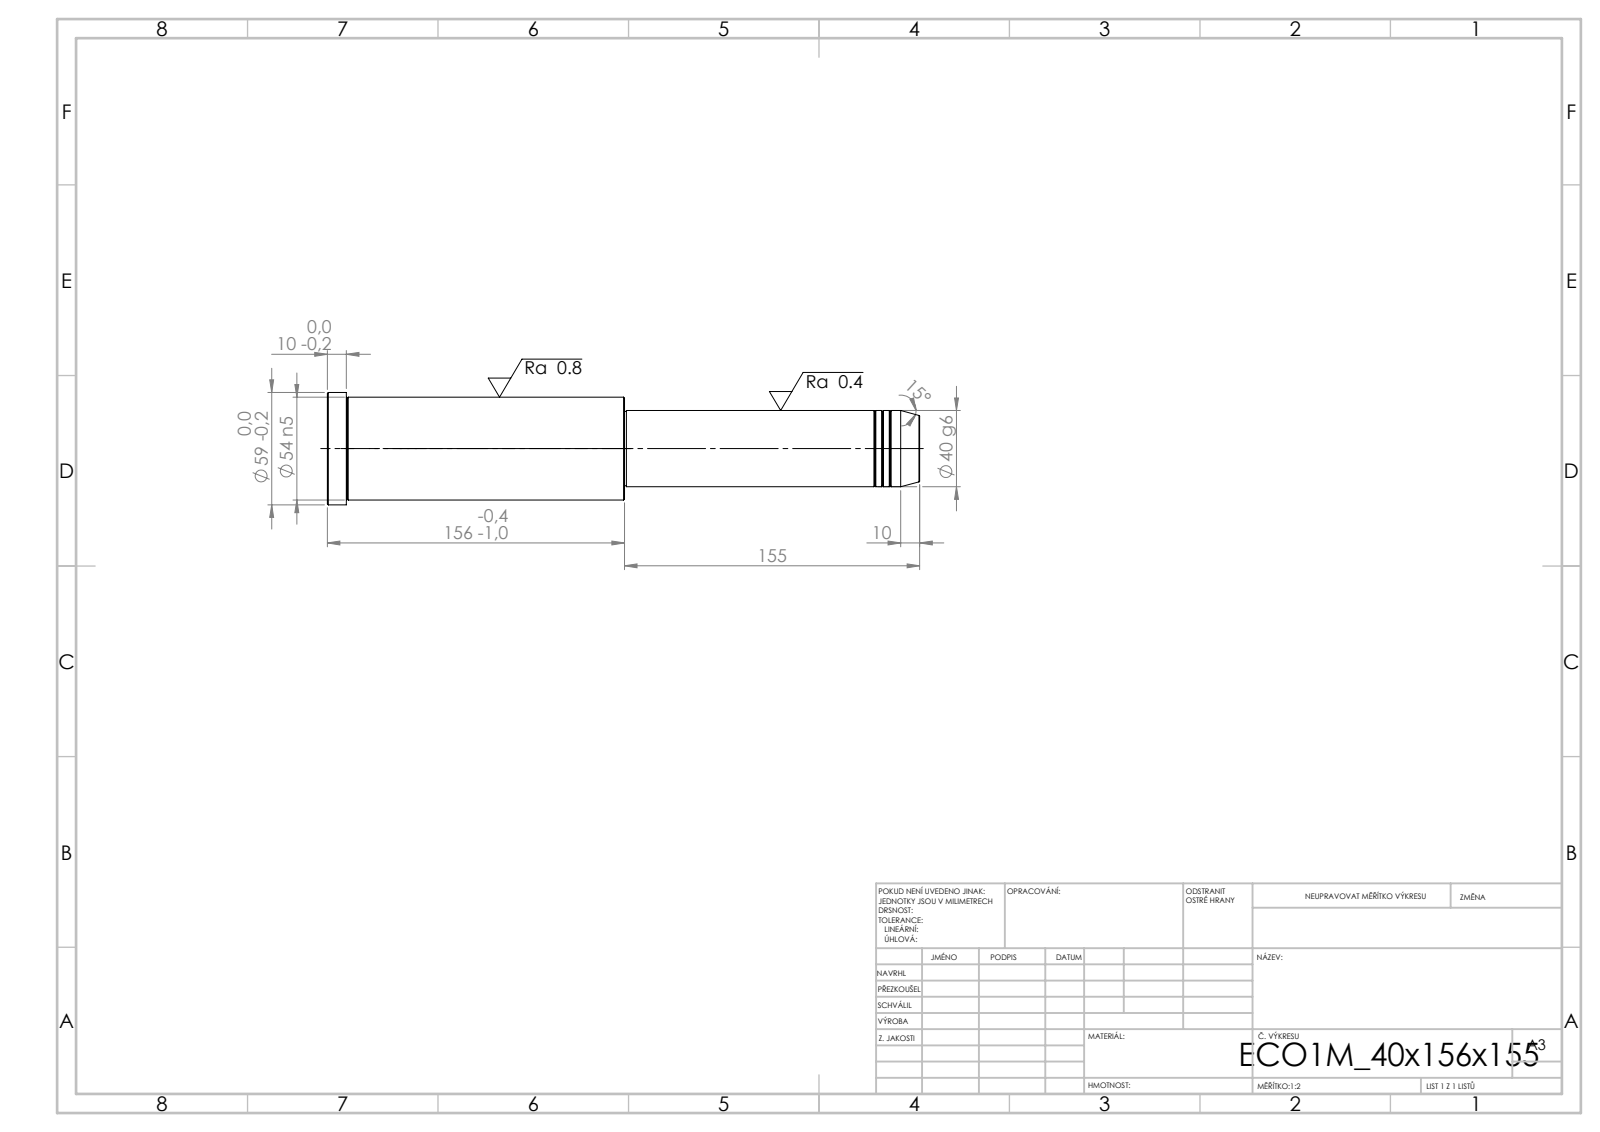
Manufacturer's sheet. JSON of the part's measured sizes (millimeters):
{"step_written_by": "SolidWorks 2019 (CONFIG_CONTROL_DESIGN)", "units": "millimeters", "bodies": {"solids": 1, "faces": 43, "planar": 5, "cylindrical": 14, "other": 24}, "overall_size": [311, 59, 59], "volume_mm3": 554561, "surface_area_mm2": 51514, "round_bosses_or_shafts": [[59, 1], [54, 1], [40, 1], [39, 1]], "face_to_face_distances": [156, 155, 311, 301, 146, 10, 154, 1, 147, 157]}
